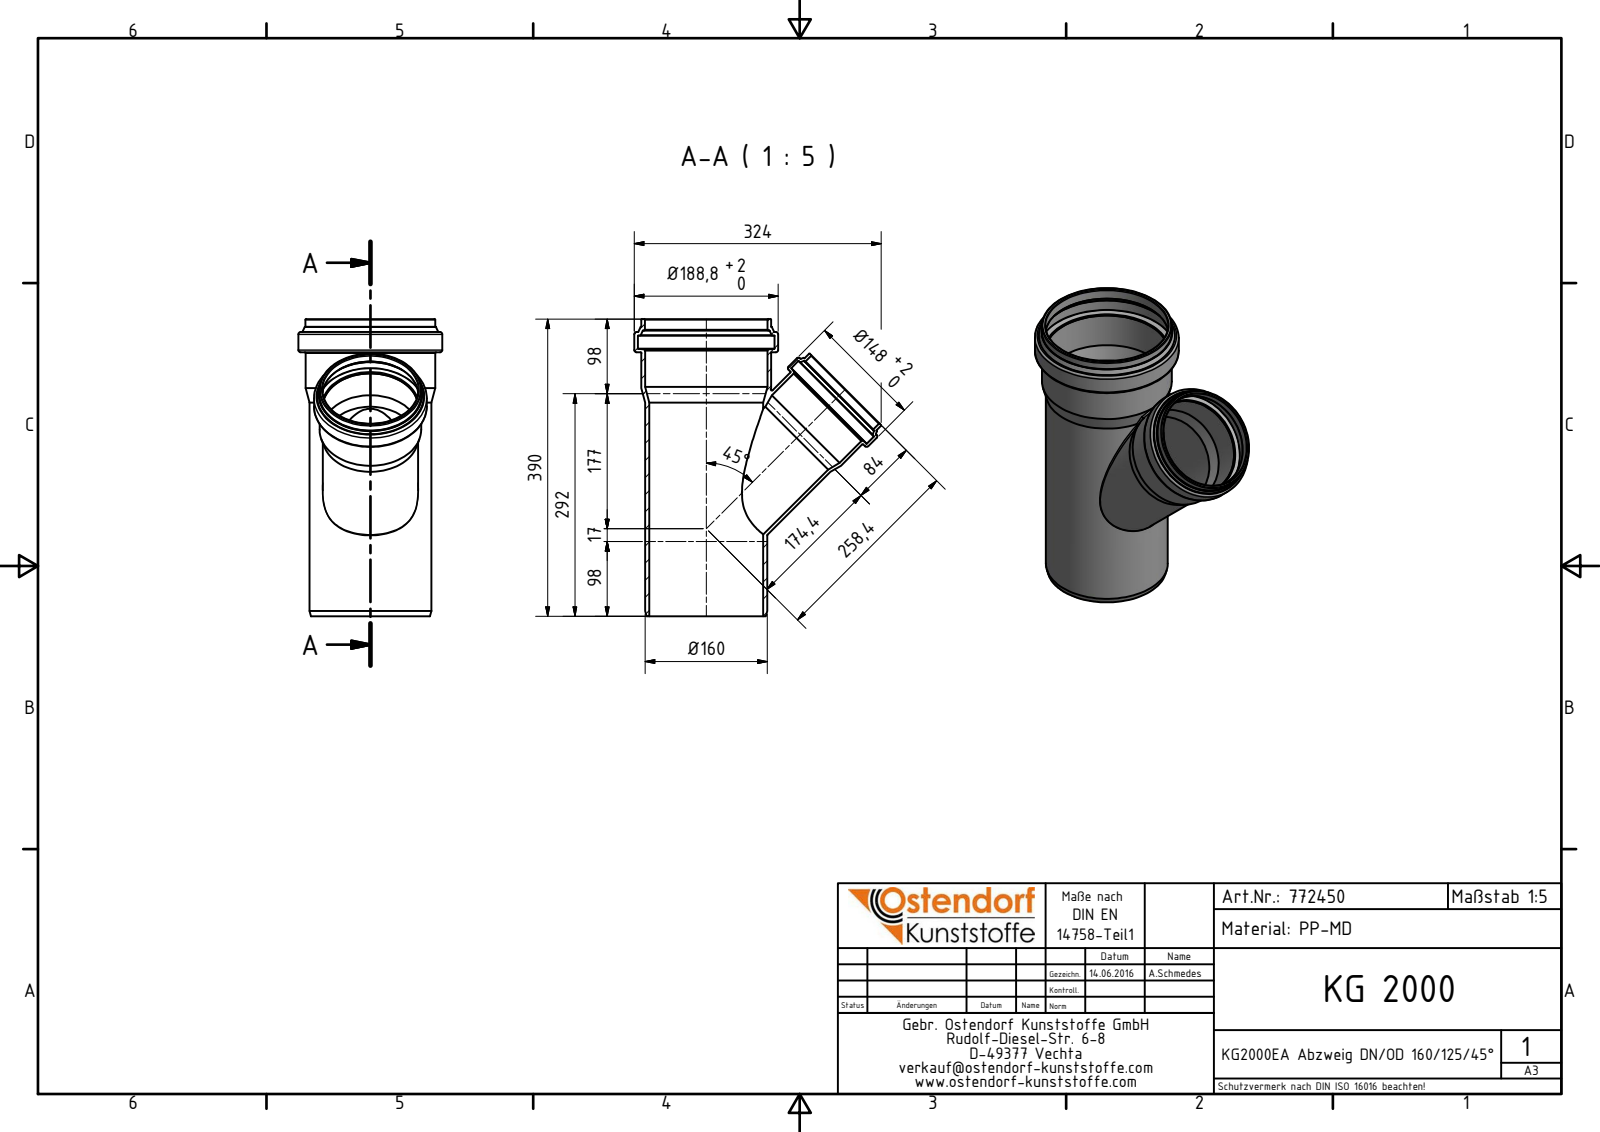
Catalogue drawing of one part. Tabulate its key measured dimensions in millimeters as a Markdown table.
| quantity | value |
| --- | --- |
| part name | 772450 KG2000EA Abzweig DN_OD 160_125_45° |
| STEP written by | Autodesk Inventor 2016 (AUTOMOTIVE_DESIGN) |
| units | millimeters |
| bodies | 1 solid, 76 faces (11 planar, 18 cylindrical, 47 other) |
| overall size | 390 × 324 × 188.8 |
| volume | 1 221 000 mm³ |
| surface area | 515 405 mm² |
| round holes (diameter × count) | 116.61 × 1, 125.6 × 1, 125.9 × 1, 140.2 × 1, 149.7 × 1, 160.7 × 1, 161 × 1, 179.4 × 1 |
| round bosses / shafts (diameter × count) | 188.8 × 1, 170.4 × 1, 170.3 × 1, 160.1 × 1, 148 × 1, 133.7 × 1, 133.4 × 1, 125.1 × 1 |
| main face-to-face distances | 346.3, 390, 43.7, 373, 26.7, 17, 34.6, 21.3, 13.3, 25.11 |
